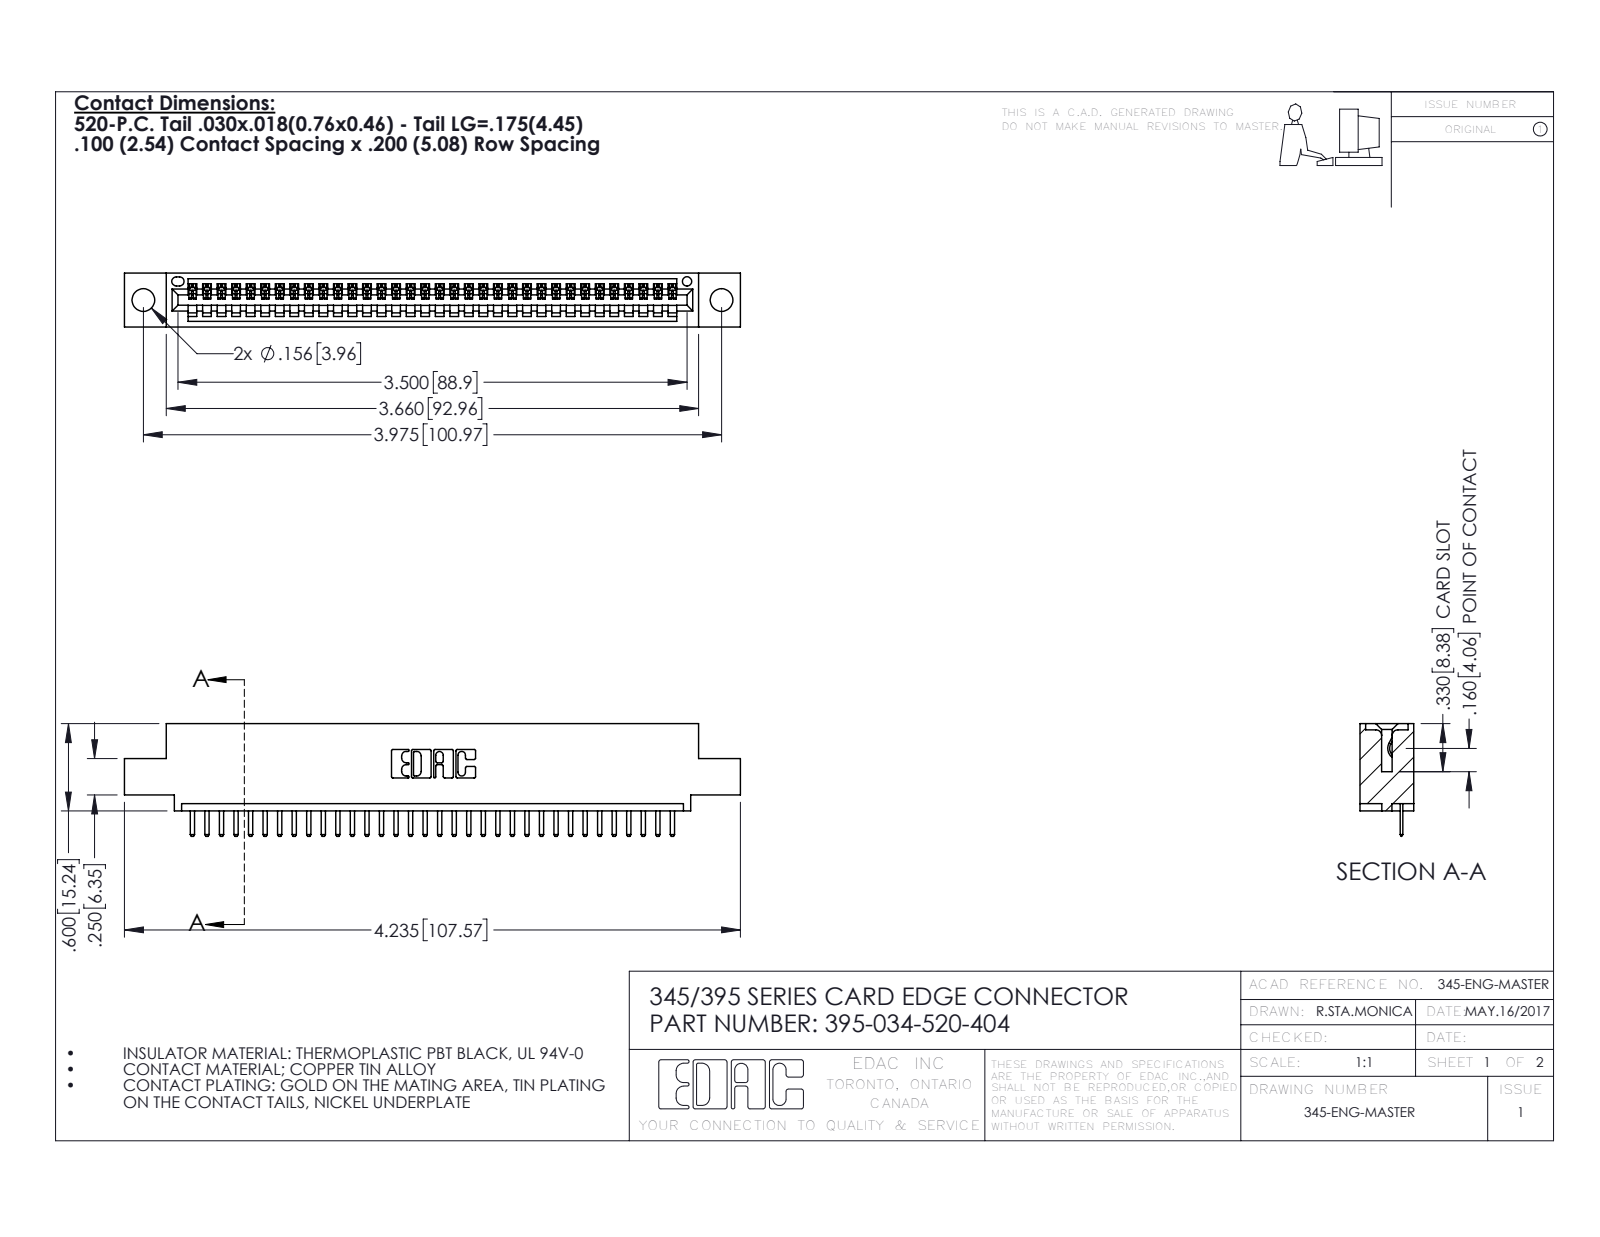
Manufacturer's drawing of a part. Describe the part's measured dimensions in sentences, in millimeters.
The part is named "345-292-001_345-293-120; 345 Part_0.110 Offset - 0.156 Dia-TH; 395-034-520-404". Its 3-D file was written by "SolidWorks 2016 (CONFIG_CONTROL_DESIGN)". It is 35 solids with 2238 faces: 1512 planar, 726 cylindrical and 0 other. Overall it measures 107.6 by 19.7 by 9.4 millimeters. Its volume is 9 900 cubic millimeters and its surface area 12 610 square millimeters. Round holes: 2 of diameter 4, 1 of diameter 1.6. Partial cylindrical surfaces (rounded edges, fillets, slot ends): 70 of radius 0.3, 68 of radius 0.2, 22 of radius 0.3, 6 of radius 0.2, 6 of radius 0.8, 3 of radius 0.7, 2 of radius 0.8, 2 of radius 1. The main face-to-face distances are 7.6, 1.8, 9.4, 5.1, 2.5, 6.9, 0.6, 5.7, 1.8, 3.8. The hole center spacings are 6.9, 95, 101.
